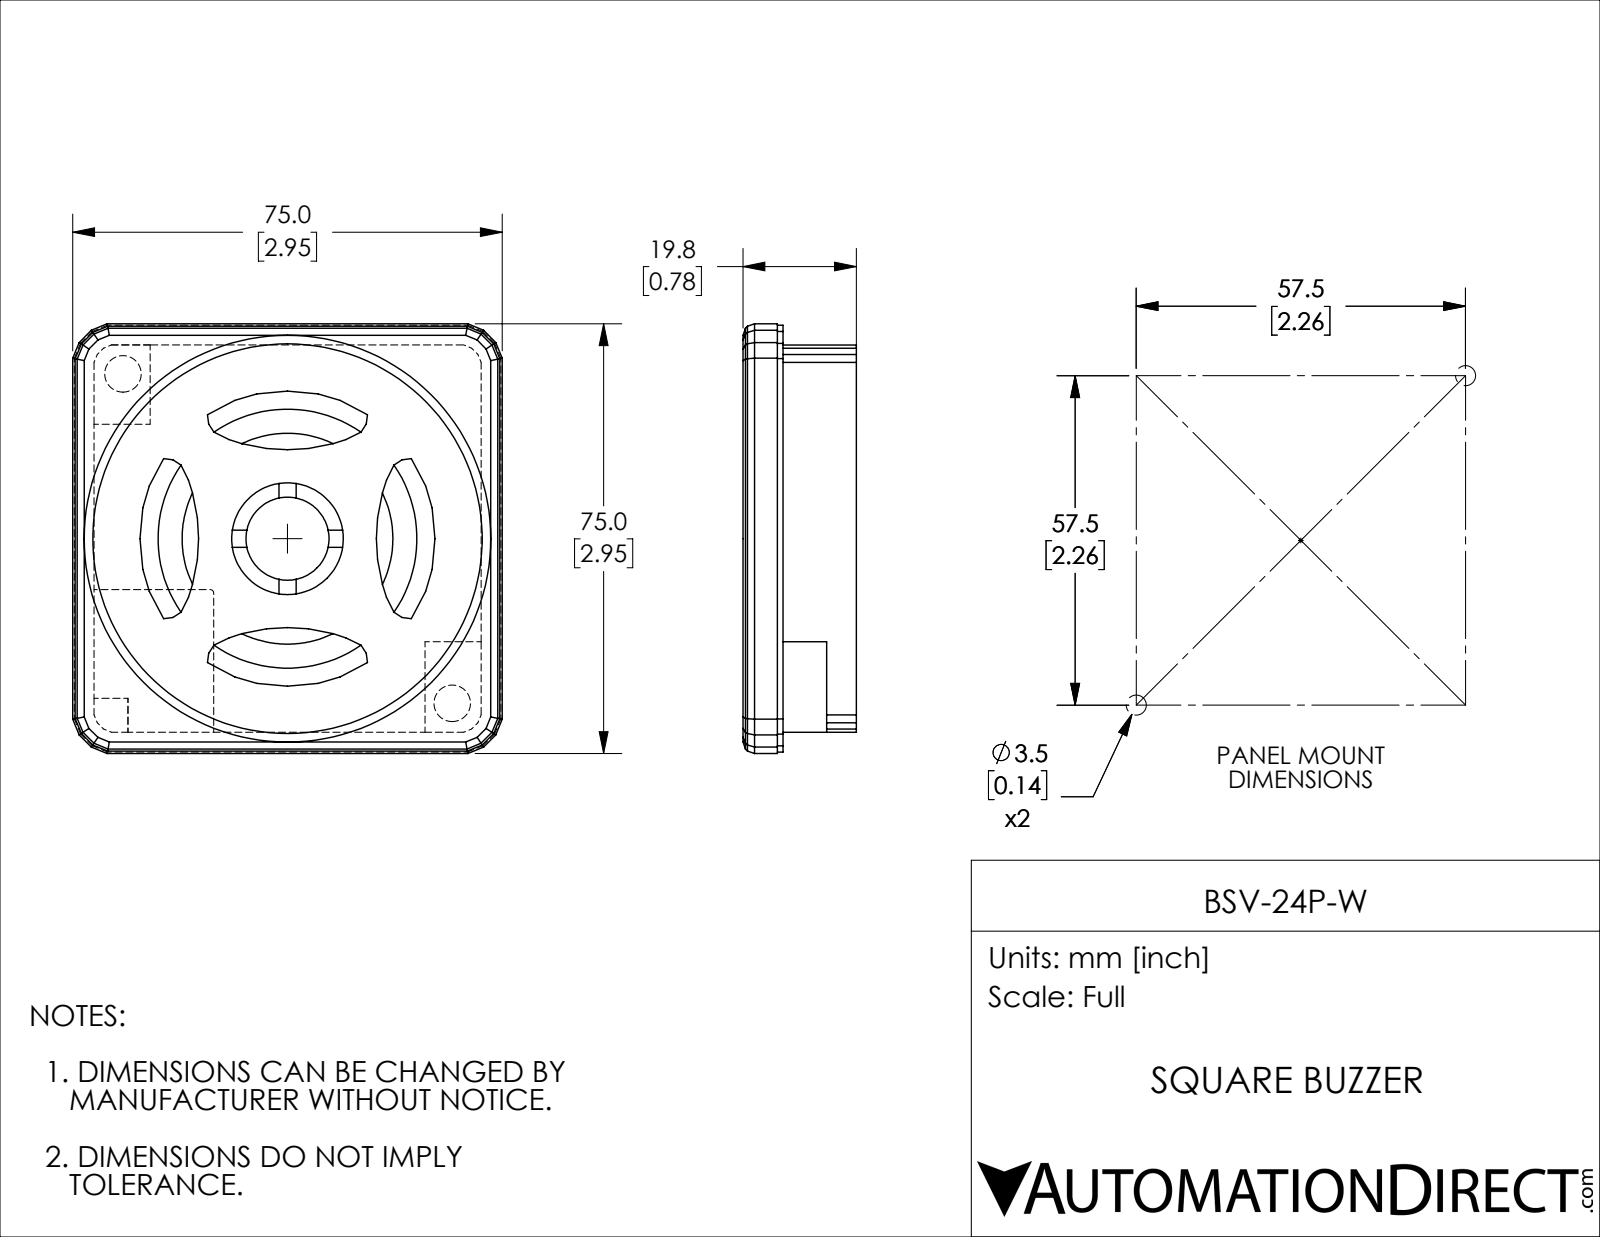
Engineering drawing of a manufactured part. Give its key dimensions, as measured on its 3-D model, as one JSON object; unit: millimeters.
{"part_name": "BSV-24P-W", "step_written_by": "SolidWorks 2018 (AUTOMOTIVE_DESIGN)", "units": "millimeters", "bodies": {"solids": 1, "faces": 265, "planar": 229, "cylindrical": 21, "other": 15}, "overall_size": [75, 75, 19.8], "volume_mm3": 89830, "surface_area_mm2": 18470, "round_holes": [[6.4, 2]], "round_bosses_or_shafts": [[68, 1]], "partial_cylinders_radius": [[7.2, 1], [9.8, 1], [22.6, 1]], "face_to_face_distances": [19.8, 67.6, 3.7, 71.3, 7, 12.8, 1, 3, 4, 2], "hole_center_spacings": [81.3]}
